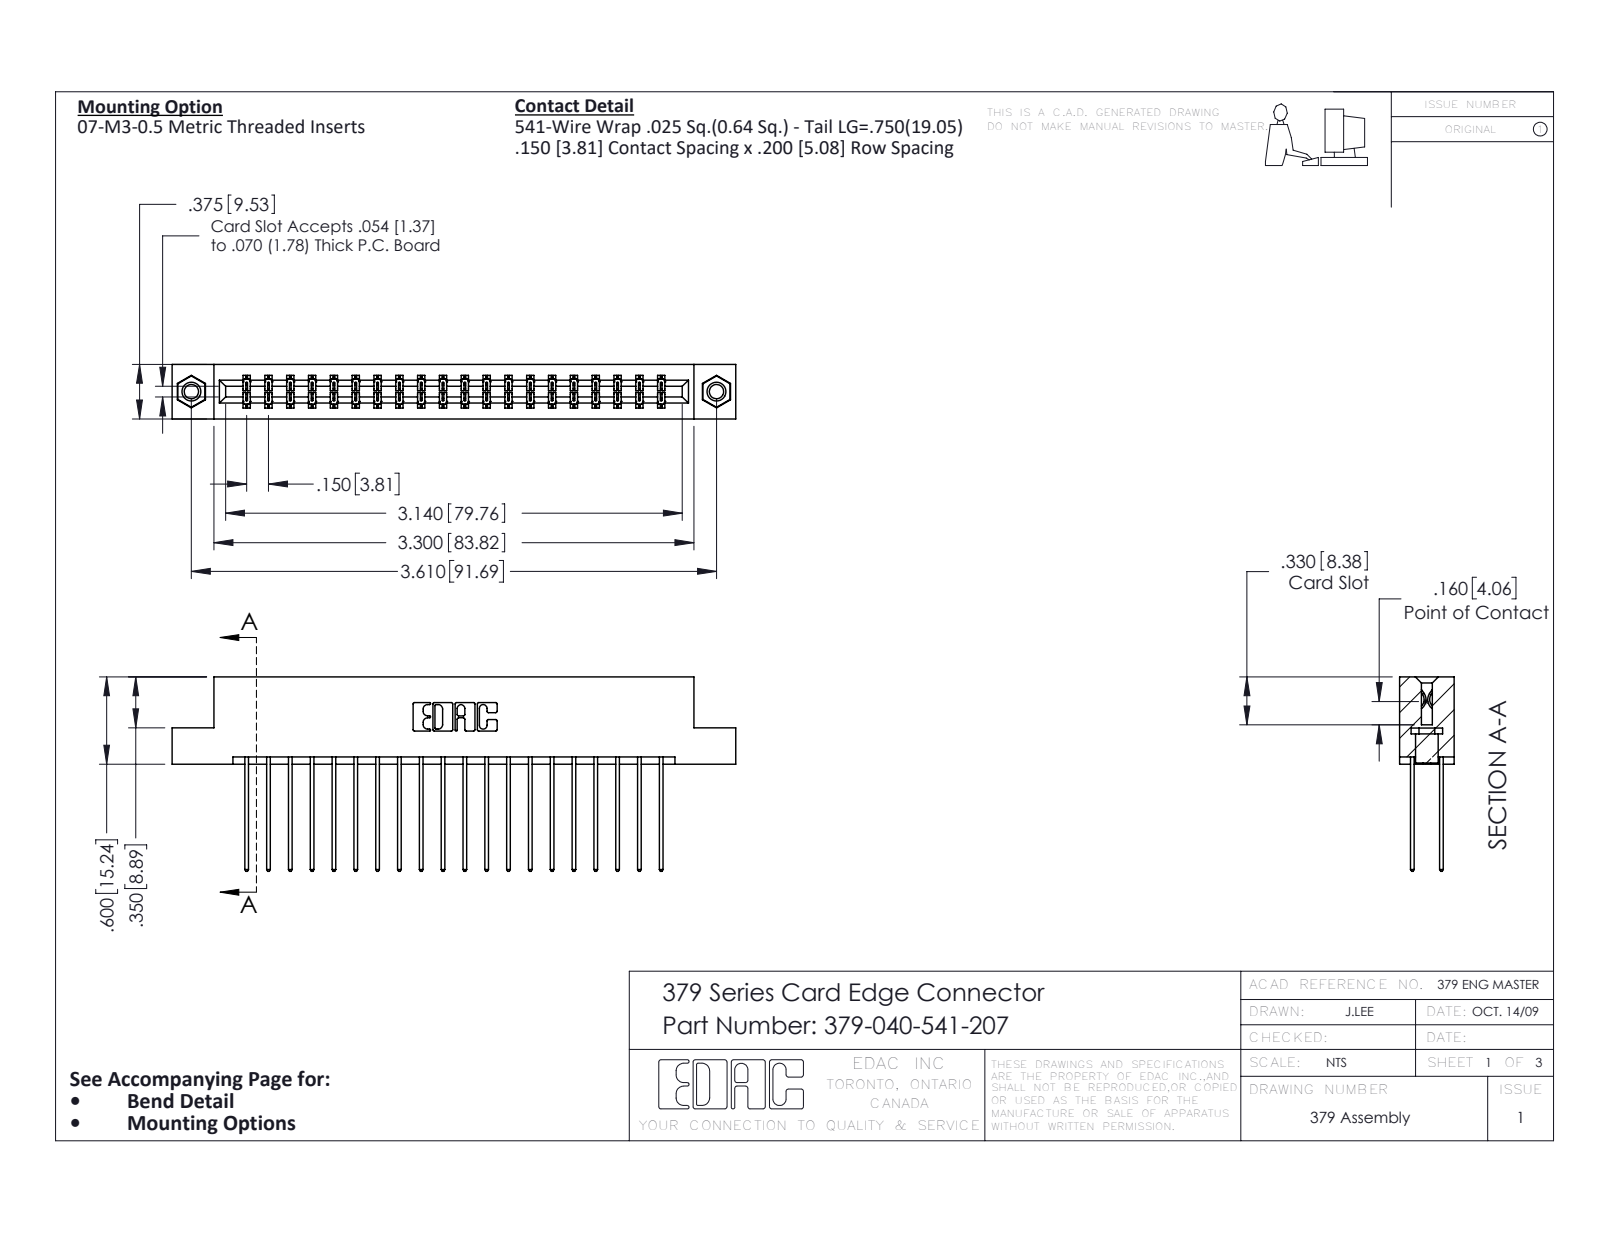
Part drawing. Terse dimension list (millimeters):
name: 345-292-001_345-293-141; 379-040-541-207; 345-250-001_345-250-005-103; 379 Part_Flush - .156 Dia - TI
written by: SolidWorks 2016 (CONFIG_CONTROL_DESIGN)
unit: mm
bodies: 43 solids, 2254 faces (1542 planar, 696 cylindrical, 16 other)
size: 98.4 × 34 × 9.5
volume: 10 400 mm³; area: 12 700 mm²
holes: 2× ⌀2.5, 2× ⌀3.2, 2× ⌀4
bosses: 2× ⌀3.9
rounds: 60× R0.2, 40× R0.3, 22× R0.3, 6× R0.2, 6× R0.8, 3× R0.7, 2× R0.4, 2× R0.6
face distances: 7.6, 1.9, 5.1, 2.5, 9.5, 7, 0.6, 1.9, 3.8, 5.7
hole spacings: 91.7
